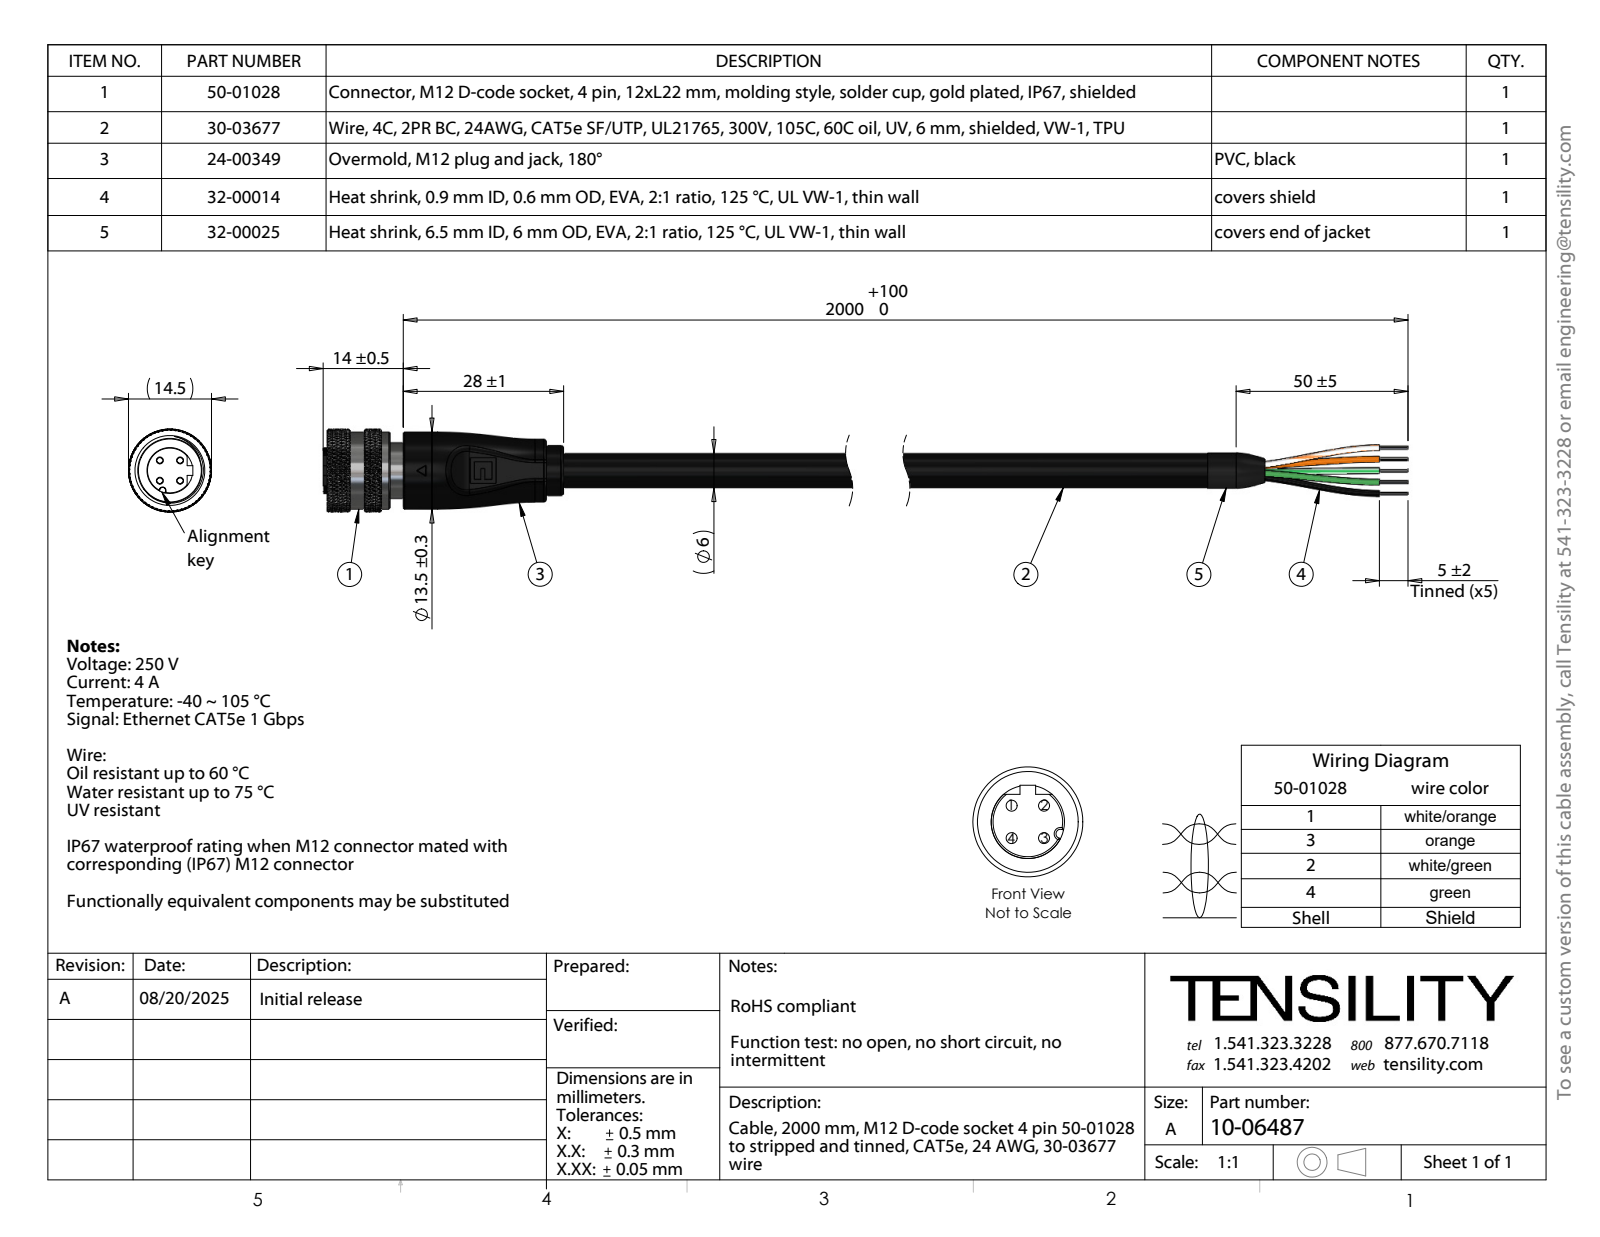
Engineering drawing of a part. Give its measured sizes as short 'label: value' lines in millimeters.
name: 30-03677_s + t; 50-01028-01_默认; 10-06487; 50-01028_默认 (+5 more)
written by: SolidWorks 2025 (CONFIG_CONTROL_DESIGN)
unit: mm
bodies: 87 solids, 3550 faces (339 planar, 940 cylindrical, 2271 other)
size: 222 × 14.5 × 14.5
volume: 9 616 mm³; area: 27 027 mm²
holes: 28× ⌀0.2, 4× ⌀1.05, 4× ⌀1.1, 4× ⌀1.2, 1× ⌀3.16, 1× ⌀3.21, 1× ⌀3.36, 1× ⌀9, 1× ⌀10, 1× ⌀11.2
bosses: 35× ⌀0.2, 4× ⌀1.6, 4× ⌀1.5, 1× ⌀13.5, 1× ⌀11, 1× ⌀10.6, 1× ⌀10.5, 1× ⌀9.8
rounds: 10× R0.1, 6× R0.4, 2× R0.5, 2× R1.5, 1× R4, 1× R5, 1× R5.58, 1× R6.75
face distances: 178, 28, 150, 7, 4.7, 1, 31.8, 3.5, 23.3, 173.3
hole spacings: 1.91, 0.36, 2.09, 1.06, 0.89, 1.08, 1.24, 1.8
